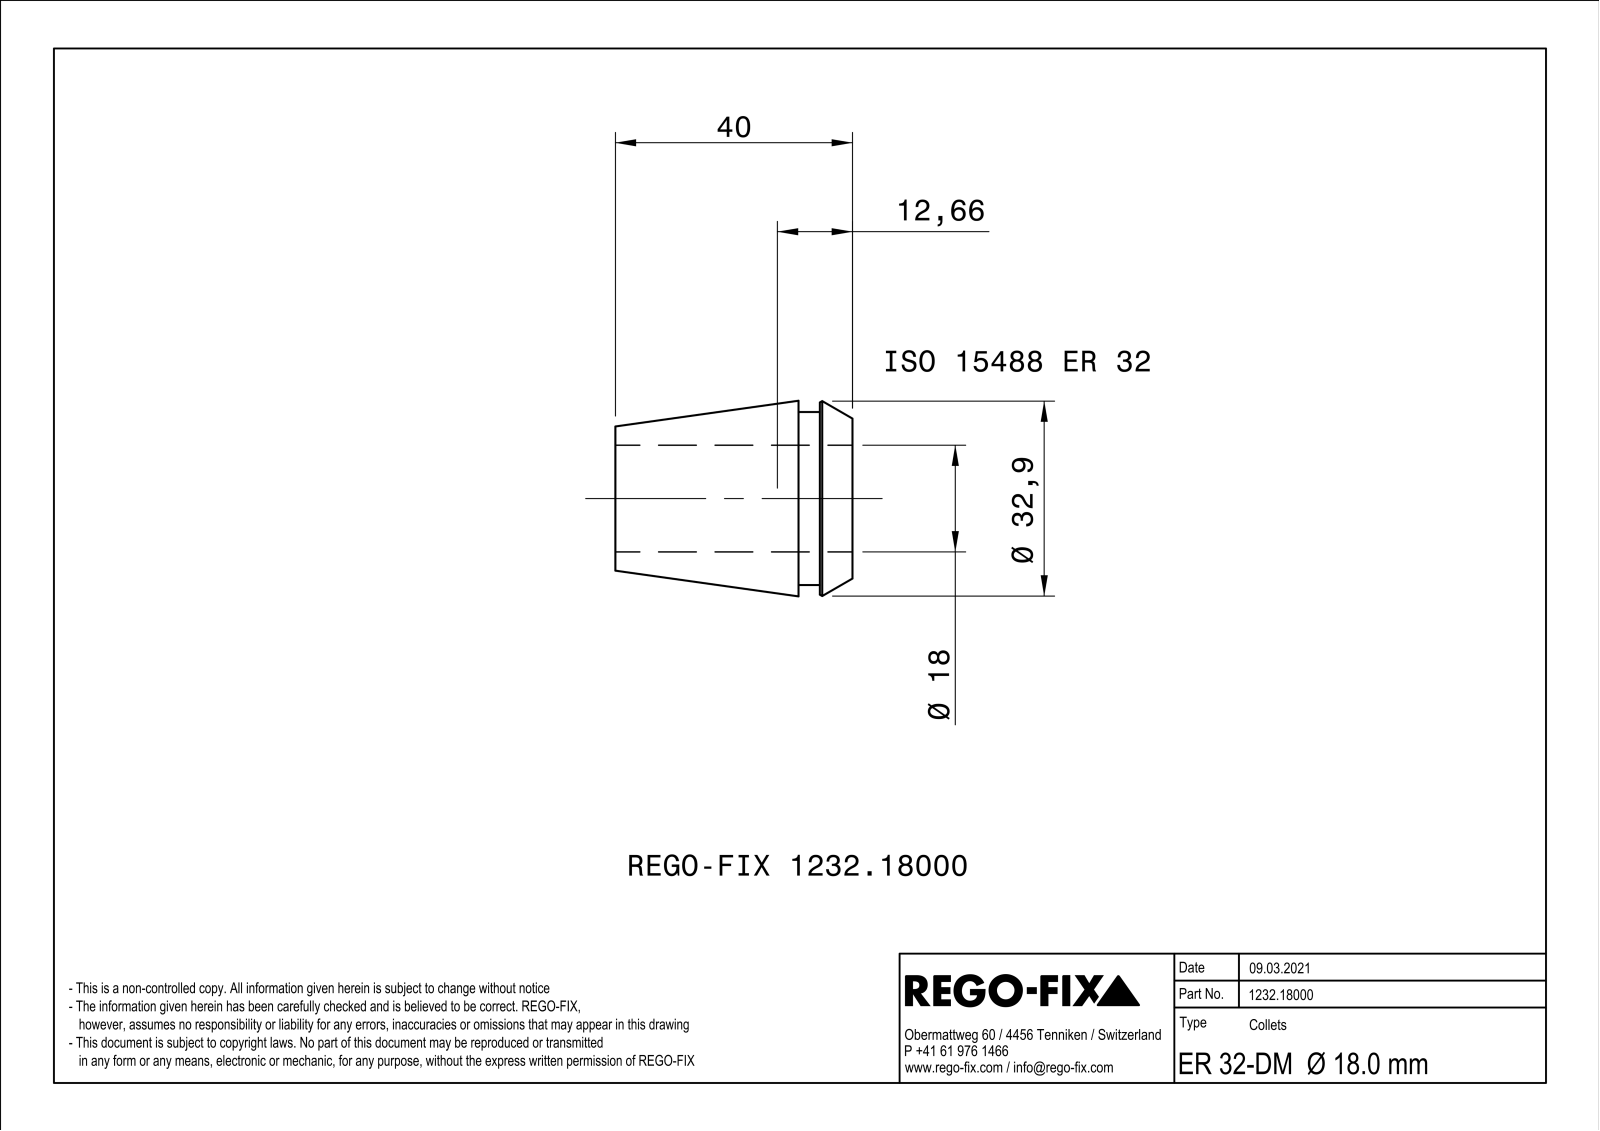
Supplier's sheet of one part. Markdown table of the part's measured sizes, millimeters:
| quantity | value |
| --- | --- |
| part name | NOCUT |
| STEP written by | SIEMENS PLM Software Solid Edge ST10 (AUTOMOTIVE_DESIGN) |
| units | millimeters |
| bodies | 1 solid, 154 faces (80 planar, 9 cylindrical, 65 other) |
| overall size | 40 × 32.98 × 32.98 |
| volume | 13 715 mm³ |
| surface area | 10 956 mm² |
| round holes (diameter × count) | 18 × 1 |
| round bosses / shafts (diameter × count) | 29.2 × 1 |
| main face-to-face distances | 1, 40, 9.1, 30.9, 5.5, 3.6, 34.5, 16, 10.5, 6.9 |
